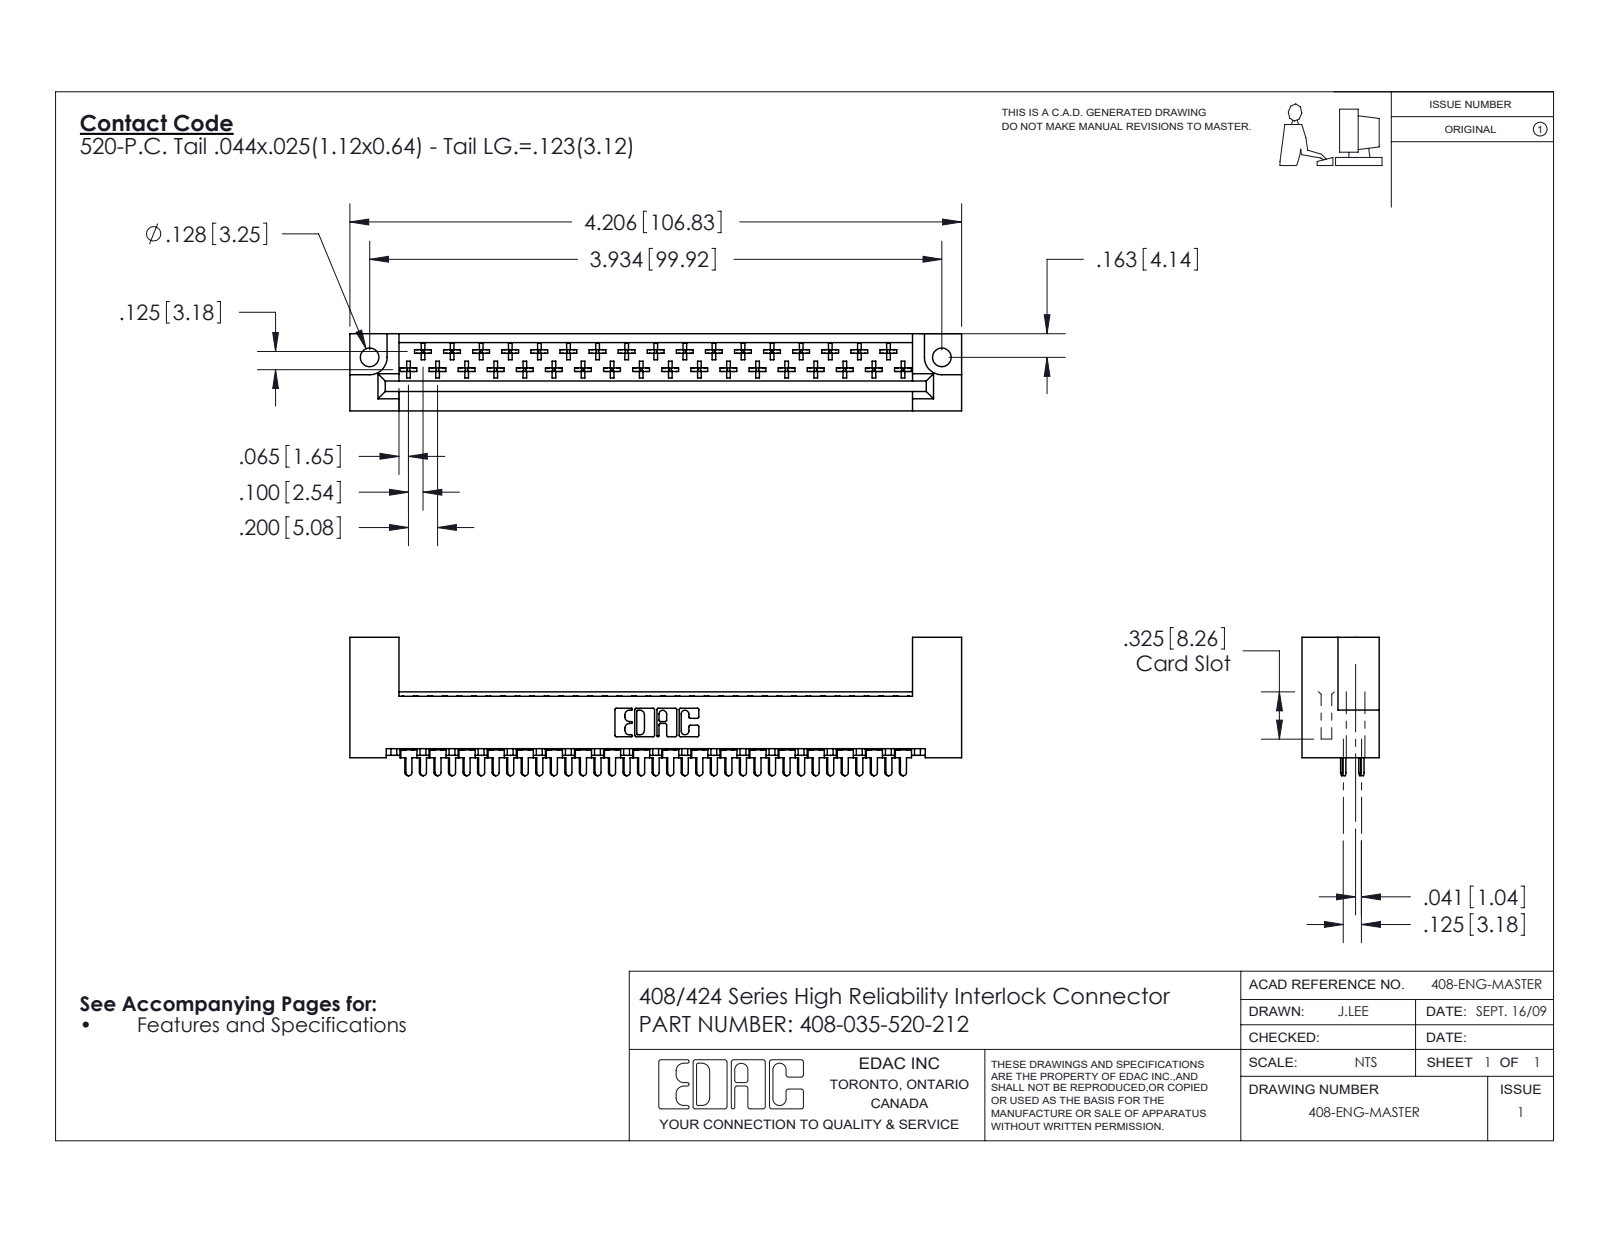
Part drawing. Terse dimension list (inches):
name: 408-035-520-212; 408-290-001_408-290-120; 408 Part_035 - 2
written by: SolidWorks 2016 (CONFIG_CONTROL_DESIGN)
unit: in
bodies: 36 solids, 2064 faces (1559 planar, 365 cylindrical, 140 other)
size: 4.206 × 0.951 × 0.531
volume: 0.813 in³; area: 23.72 in²
holes: 2× ⌀0.128
rounds: 210× R0.01, 37× R0.02, 35× R0.022, 22× R0.01, 6× R0.007, 6× R0.031, 3× R0.026, 2× R0.12
face distances: 0.531, 0.125, 0.1, 0.025, 0.025, 0.361, 0.235, 0.259, 0.398, 0.217
hole spacings: 3.934
